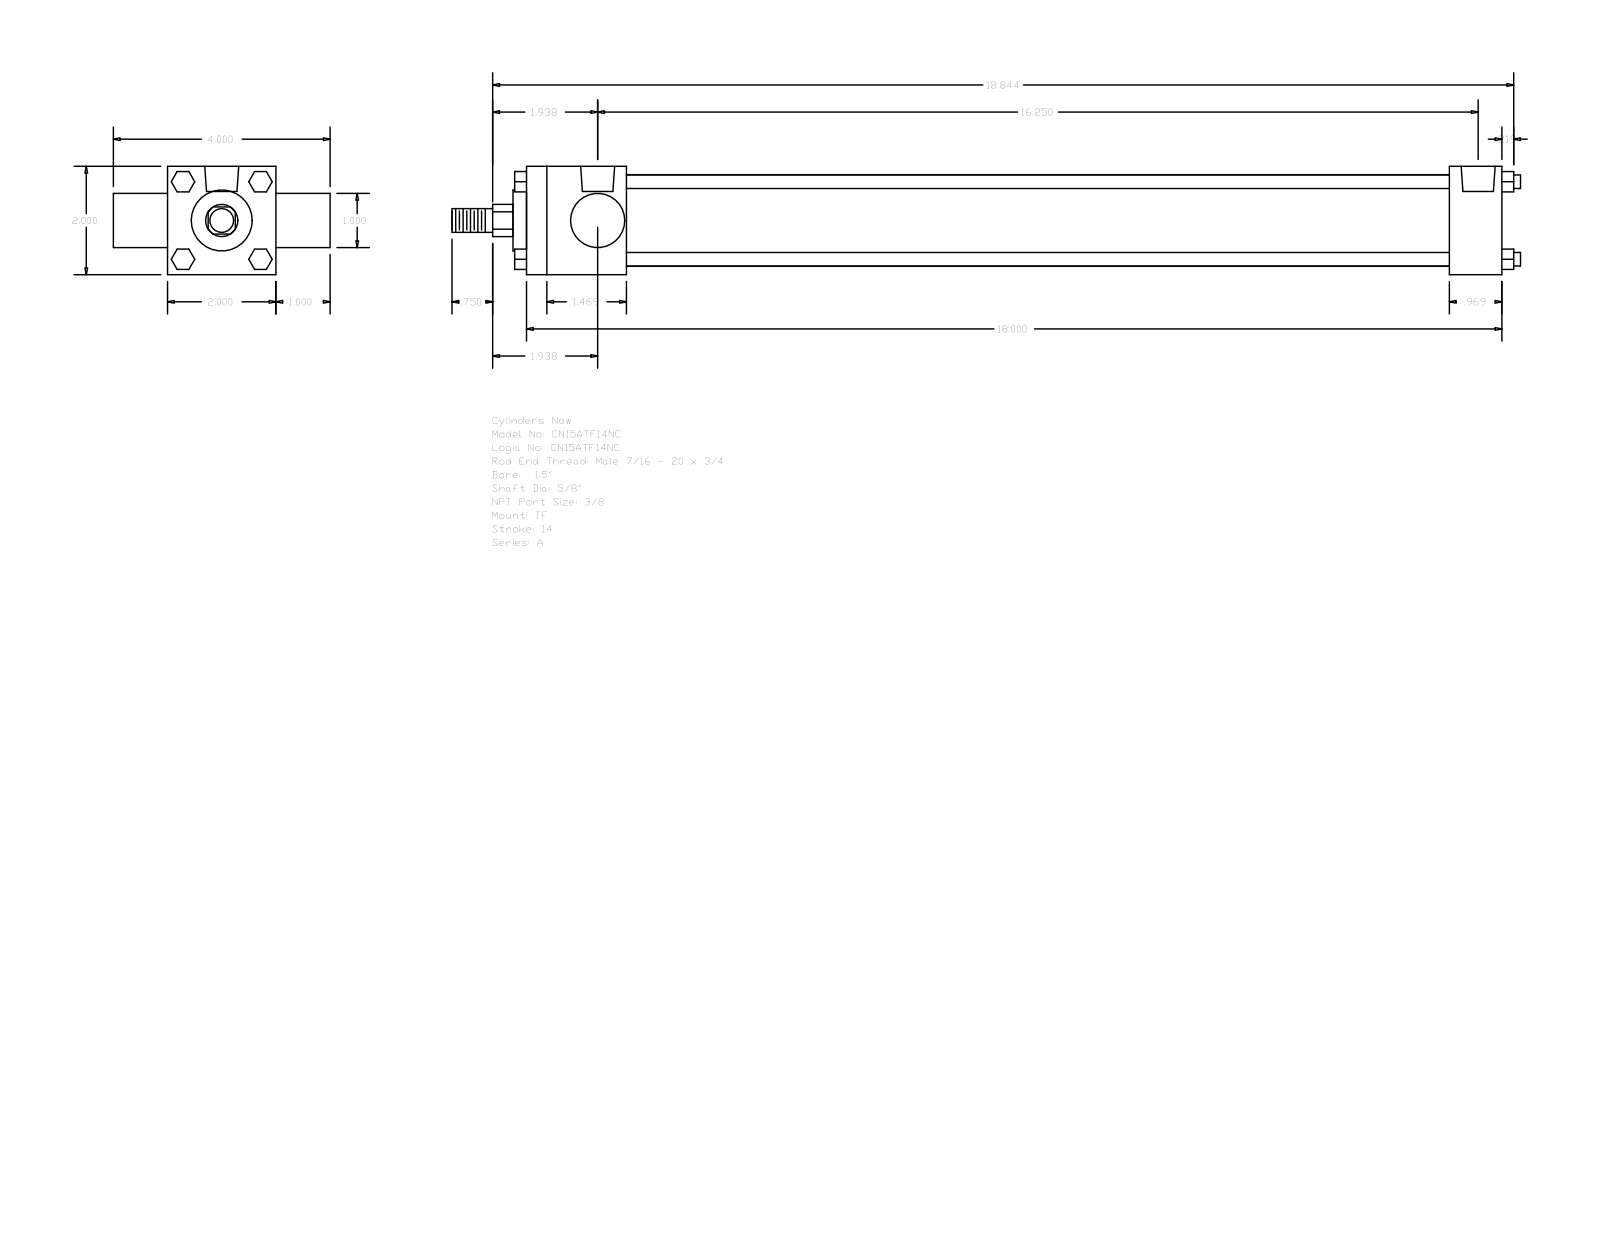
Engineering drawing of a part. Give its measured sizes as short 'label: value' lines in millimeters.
name: A_TF__0150_0.625
written by: GSSL Pune (CONFIG_CONTROL_DESIGN)
unit: mm
bodies: 0 solids, 120 faces (92 planar, 28 cylindrical, 0 other)
size: 500.86 × 101.6 × 50.8
holes: 3× ⌀5.56, 2× ⌀15.93
bosses: 4× ⌀6.35, 1× ⌀42.93, 1× ⌀28.57, 1× ⌀25.4, 1× ⌀15.88, 1× ⌀11.11
rounds: 1× R7.54
face distances: 50.8, 457.19, 25.4, 76.2, 46.83, 432.59, 385.76, 410.36, 24.6, 101.6
hole spacings: 3.97, 408.78, 404.81, 412.75
